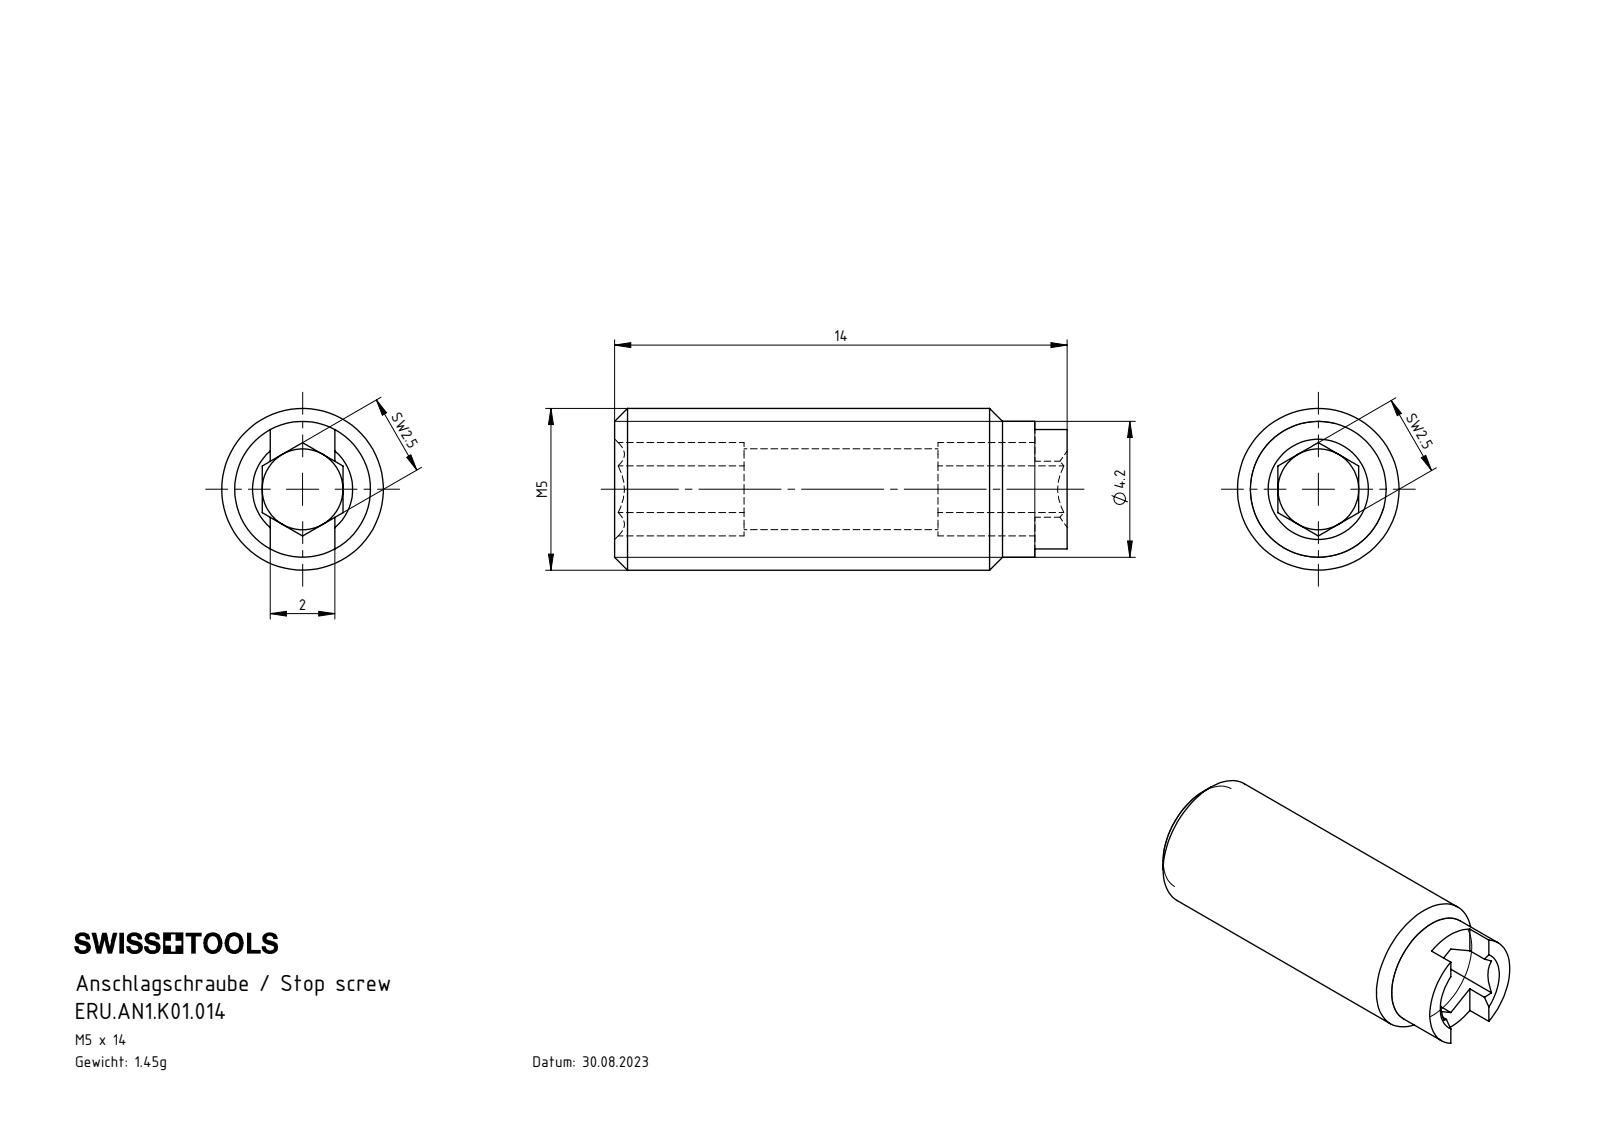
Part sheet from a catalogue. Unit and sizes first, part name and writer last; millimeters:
Units: millimetres
Overall size (bounding box): 14 × 5 × 5
Round holes (diameter × count): ⌀2.5 ×1
Round bosses / shafts (diameter × count): ⌀5 ×1, ⌀4.2 ×1
Main face-to-face distances: 2.5, 14, 2.25, 13, 1, 2, 4, 10, 6, 9
Volume: 184 mm³ · Surface area: 346 mm²
Bodies: 1 solid, 48 faces (33 planar, 6 cylindrical, 9 other)
Part name (STEP PRODUCT): ERU.AN1.K01.014
STEP written by: SolidWorks 2017 (AUTOMOTIVE_DESIGN)
